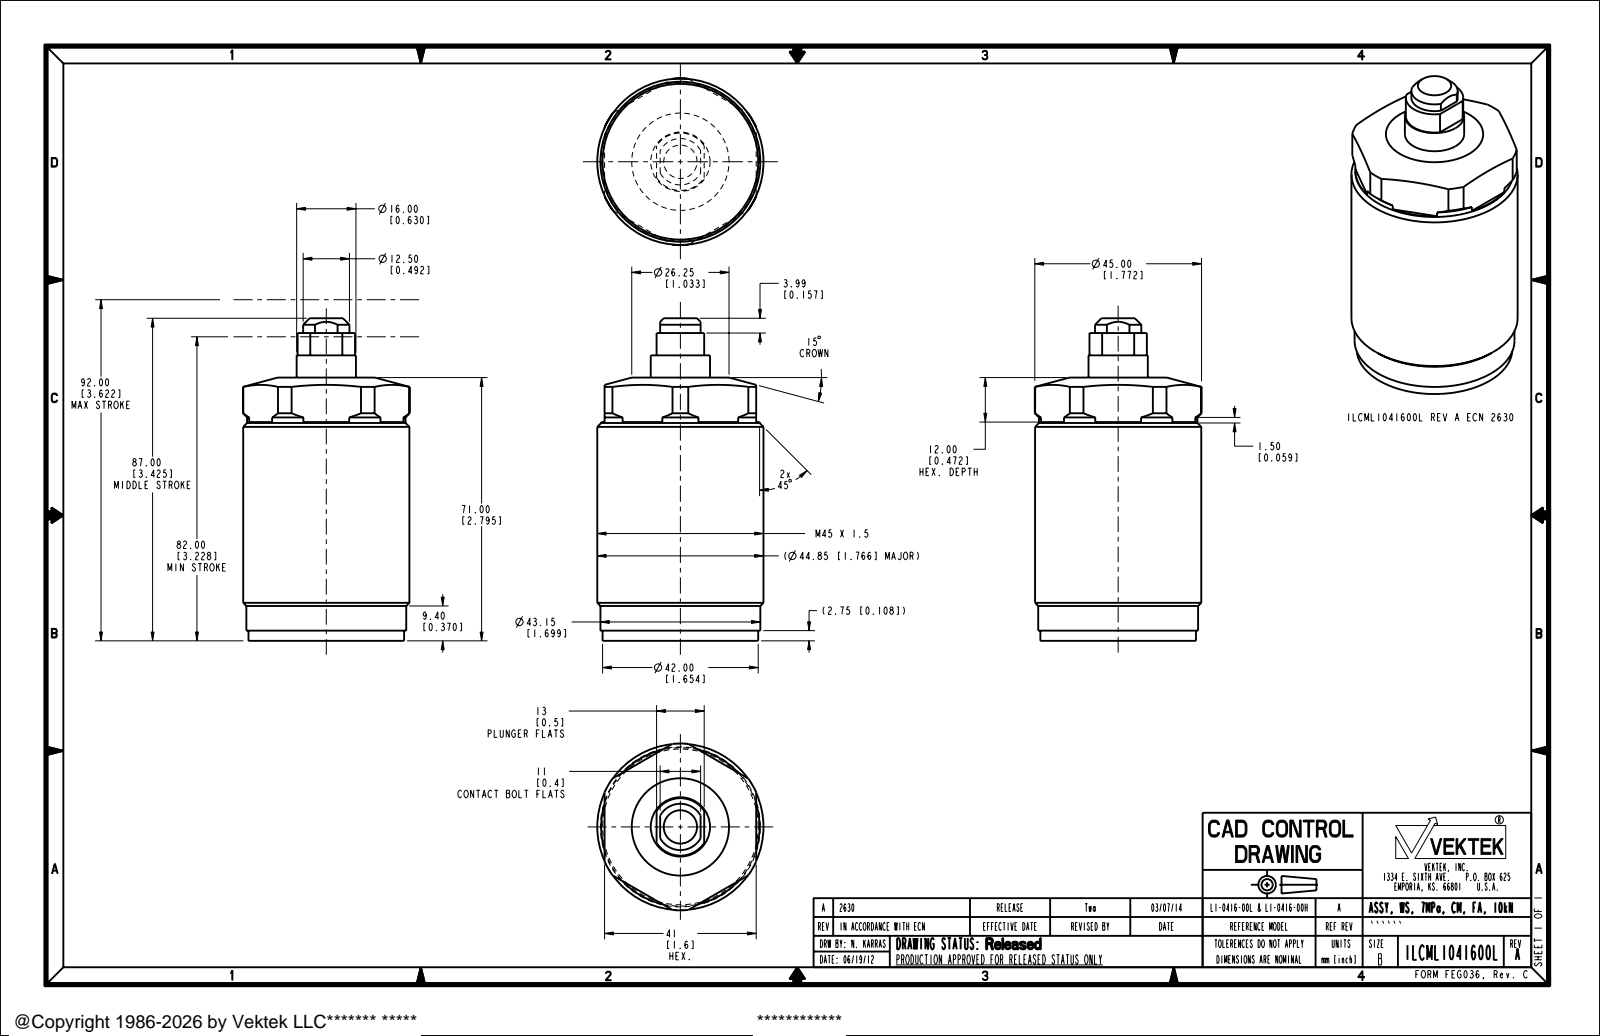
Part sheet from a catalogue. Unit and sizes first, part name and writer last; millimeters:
Units: millimetres
Overall size (bounding box): 87 × 45 × 44.85
Round bosses / shafts (diameter × count): ⌀44.85 ×1, ⌀43.15 ×1, ⌀42.75 ×1, ⌀42 ×1, ⌀16 ×1
Partial cylindrical surfaces — rounded edges, fillets, slot ends (radius × count): R6.25 ×1, R7.75 ×1, R22.5 ×1
Main face-to-face distances: 40.92, 71, 14.04, 26.88, 2.75, 68.25, 87, 84.25, 16, 83.01
Volume: 110 471 mm³ · Surface area: 13 392 mm²
Bodies: 1 solid, 56 faces (22 planar, 20 cylindrical, 14 other)
Part name (STEP PRODUCT): ILCML1041600X
STEP written by: PRO/ENGINEER BY PARAMETRIC TECHNOLOGY CORPORATION, 2013320 (AUTOMOTIVE_DESIGN)
